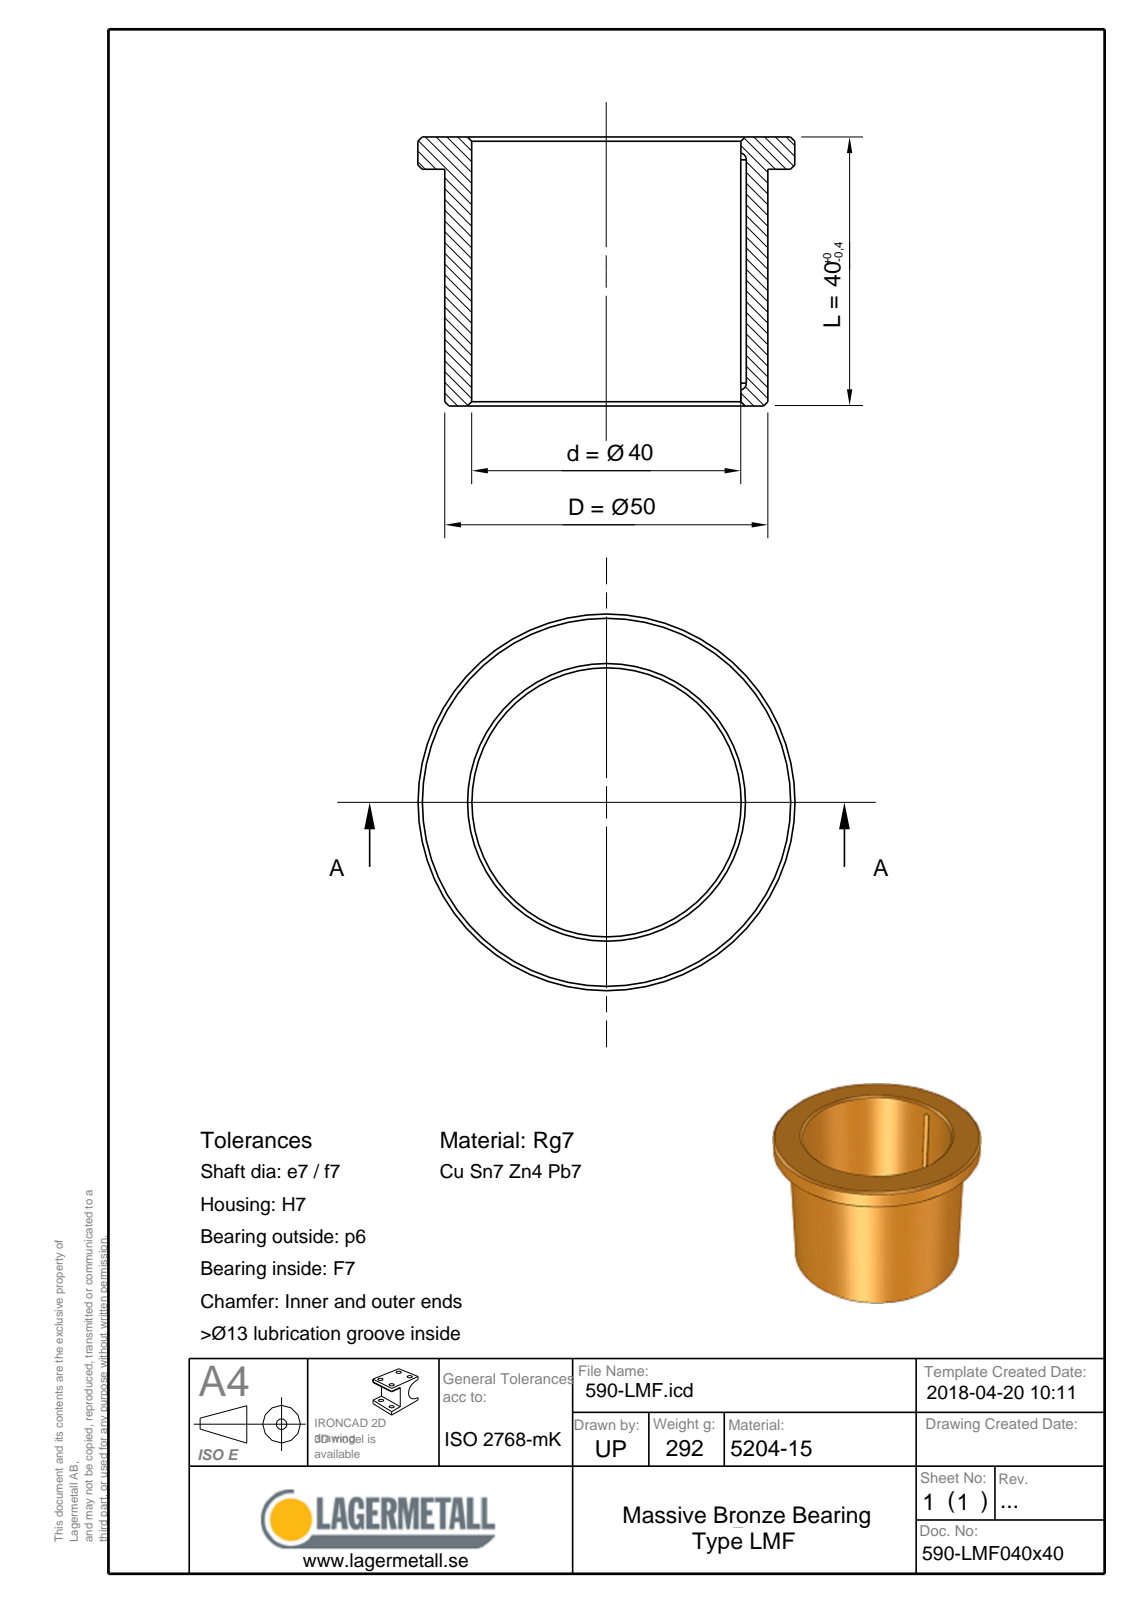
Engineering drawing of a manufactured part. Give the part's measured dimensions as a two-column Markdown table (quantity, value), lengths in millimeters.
| quantity | value |
| --- | --- |
| part name | 590-LMF040x40 |
| STEP written by | Spatial InterOp 3D (CONFIG_CONTROL_DESIGN) |
| units | millimeters |
| bodies | 1 solid, 16 faces (4 planar, 5 cylindrical, 7 other) |
| overall size | 60 × 60 × 40 |
| volume | 33 144 mm³ |
| surface area | 14 307 mm² |
| round holes (diameter × count) | 40 × 1 |
| round bosses / shafts (diameter × count) | 60 × 1, 50 × 1 |
| partial cylindrical surfaces (radius × count) | 1.25 × 2 |
| main face-to-face distances | 6, 34, 40 |
